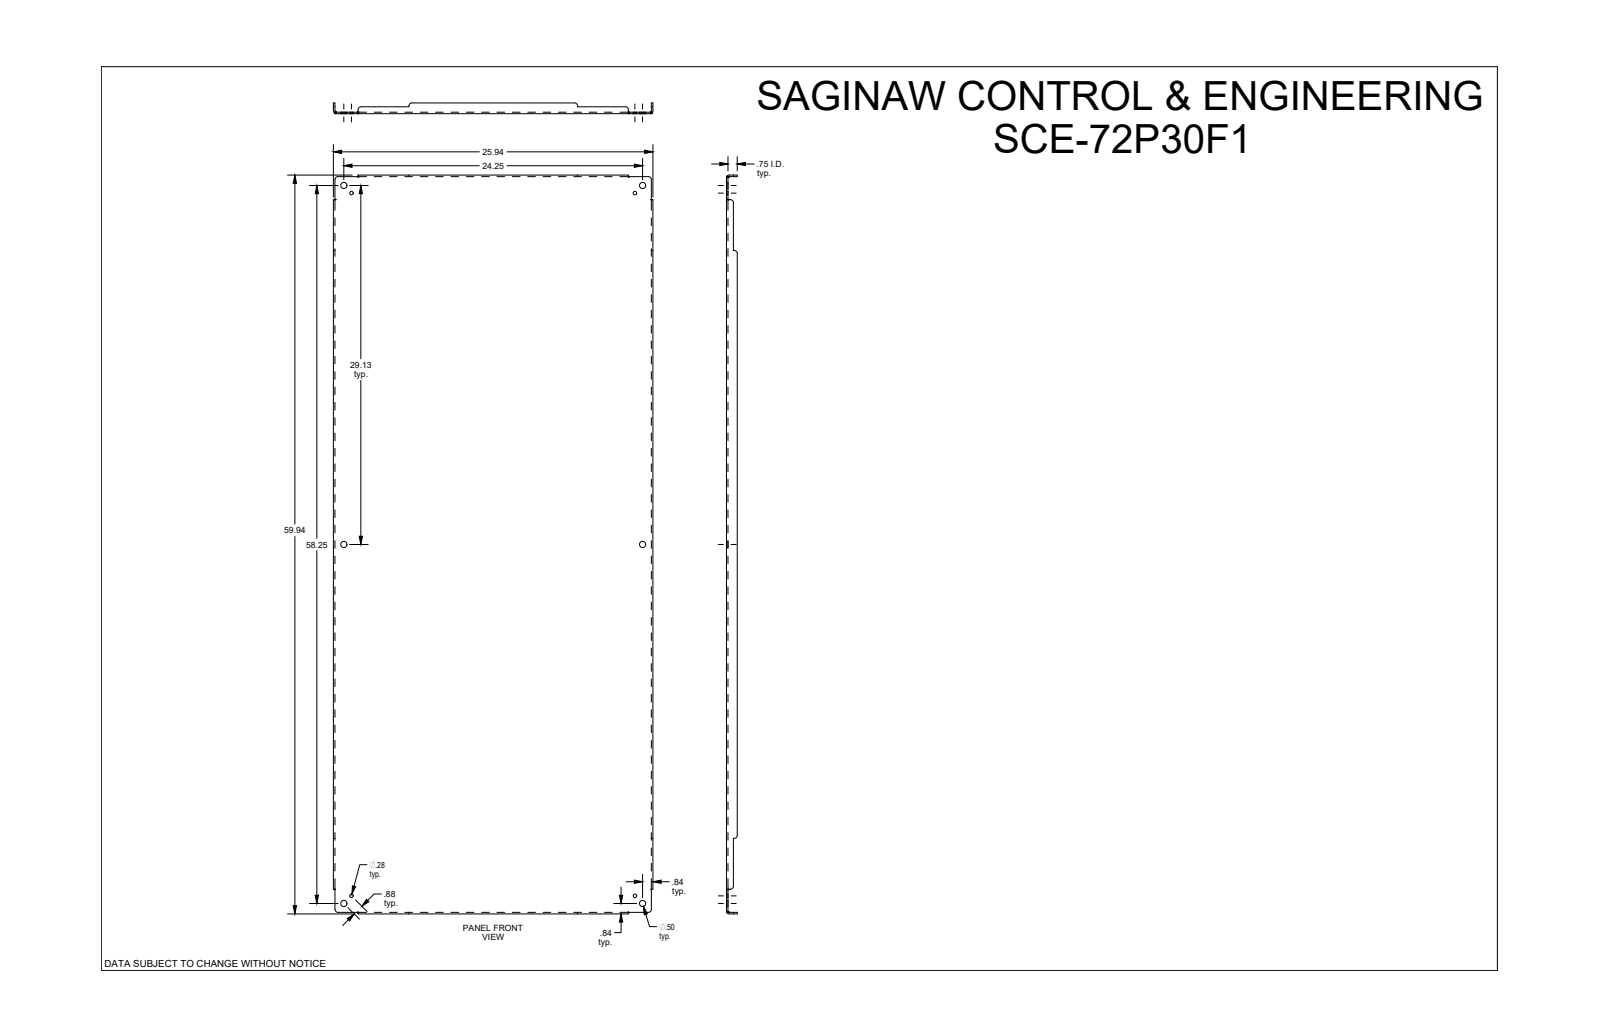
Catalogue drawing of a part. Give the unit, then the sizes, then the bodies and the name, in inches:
Units: inches
Overall size (bounding box): 59.938 × 25.938 × 0.875
Round holes (diameter × count): ⌀0.5 ×6, ⌀0.281 ×4
Partial cylindrical surfaces — rounded edges, fillets, slot ends (radius × count): R0.25 ×12, R0.112 ×4, R0.237 ×4
Main face-to-face distances: 0.125, 0.125, 25.813, 25.687, 25.938, 59.813, 0.75, 0.875, 59.687, 59.938
Hole centre spacings: 0.875, 23.639, 28.513, 29.125, 37.028, 37.898, 57.634, 62.288
Volume: 205.7 in³ · Surface area: 3 315 in²
Bodies: 1 solid, 108 faces (46 planar, 38 cylindrical, 24 other)
Part name (STEP PRODUCT): SCE-72P30F1
STEP written by: SolidWorks 2019 (CONFIG_CONTROL_DESIGN)
